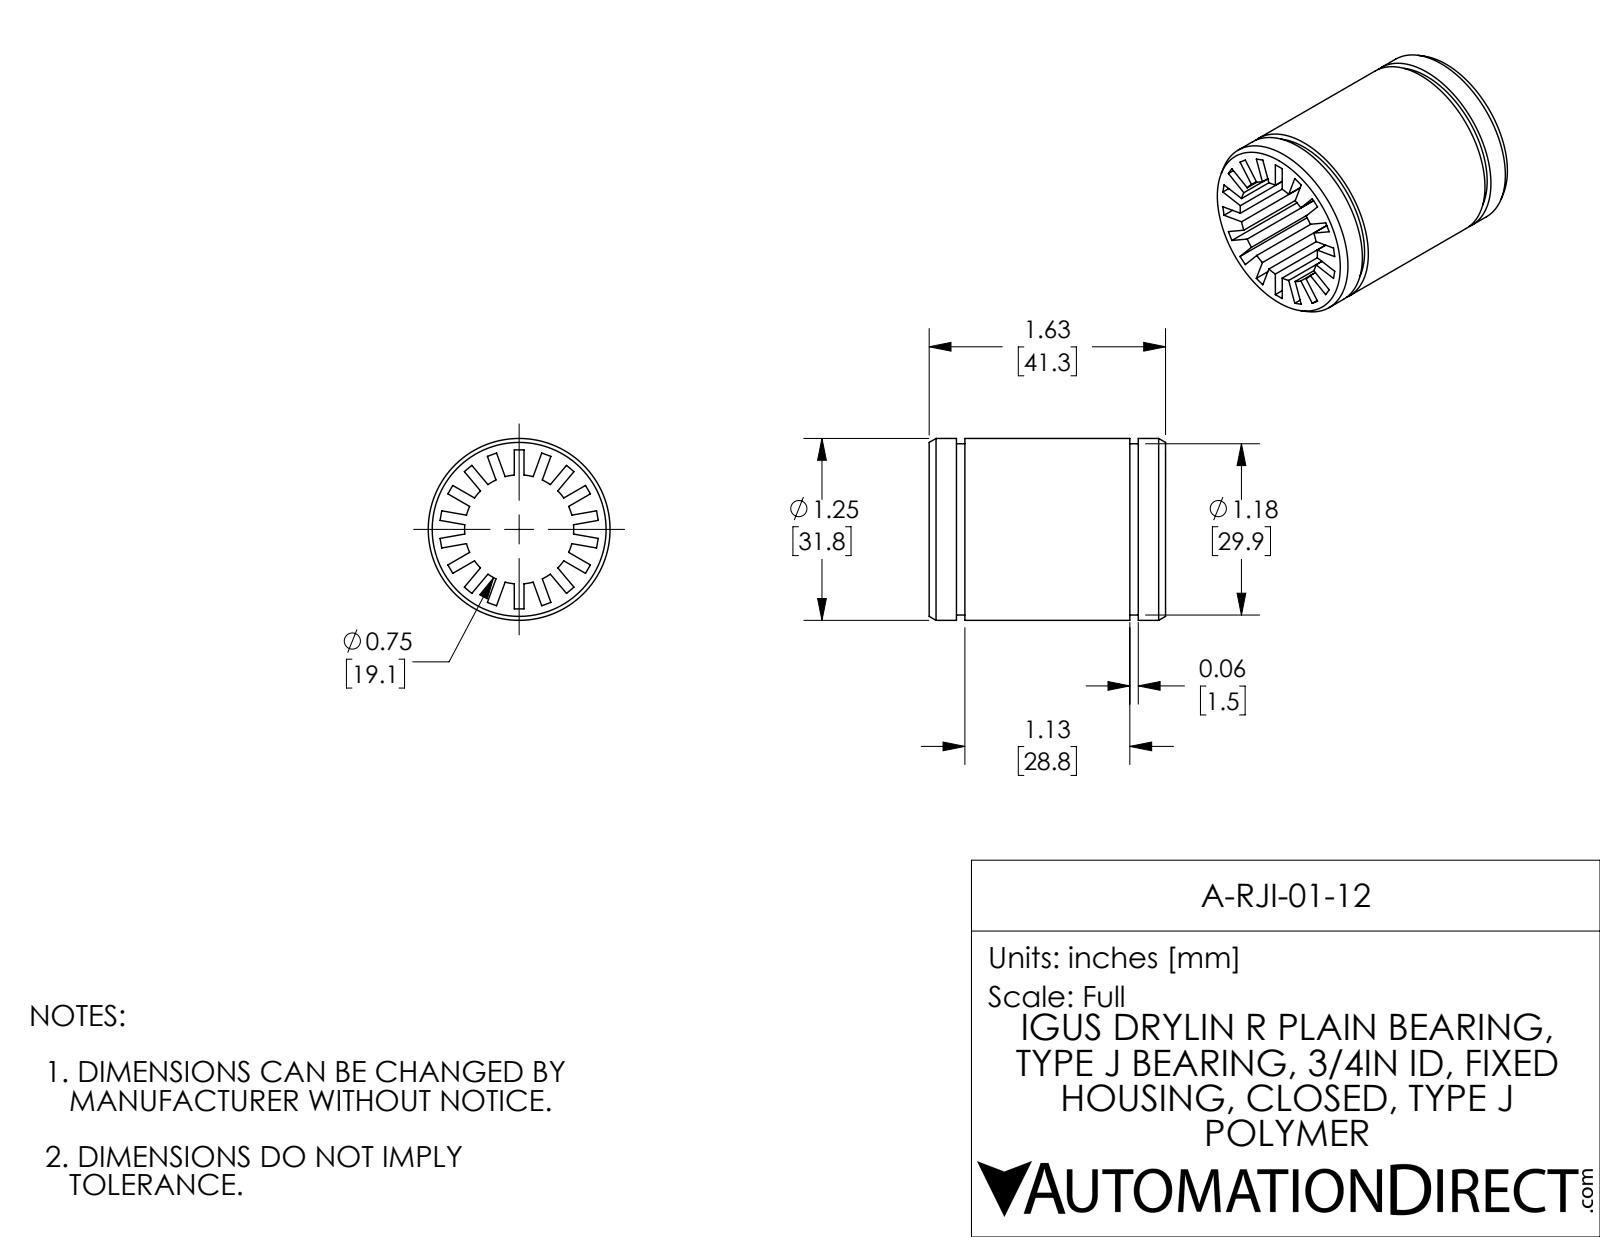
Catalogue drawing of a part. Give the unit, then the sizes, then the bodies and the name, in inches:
Units: inches
Overall size (bounding box): 1.625 × 1.25 × 1.25
Round bosses / shafts (diameter × count): ⌀1.25 ×1, ⌀1.177 ×1
Partial cylindrical surfaces — rounded edges, fillets, slot ends (radius × count): R0.375 ×1
Main face-to-face distances: 0.067, 1.093, 1.625, 0.187, 0.246, 1.38, 1.438, 1.192, 0.058, 1.092
Volume: 0.919 in³ · Surface area: 21.84 in²
Bodies: 1 solid, 92 faces (60 planar, 28 cylindrical, 4 other)
Part name (STEP PRODUCT): A-RJI-01-12
STEP written by: SolidWorks 2017 (AUTOMOTIVE_DESIGN)
